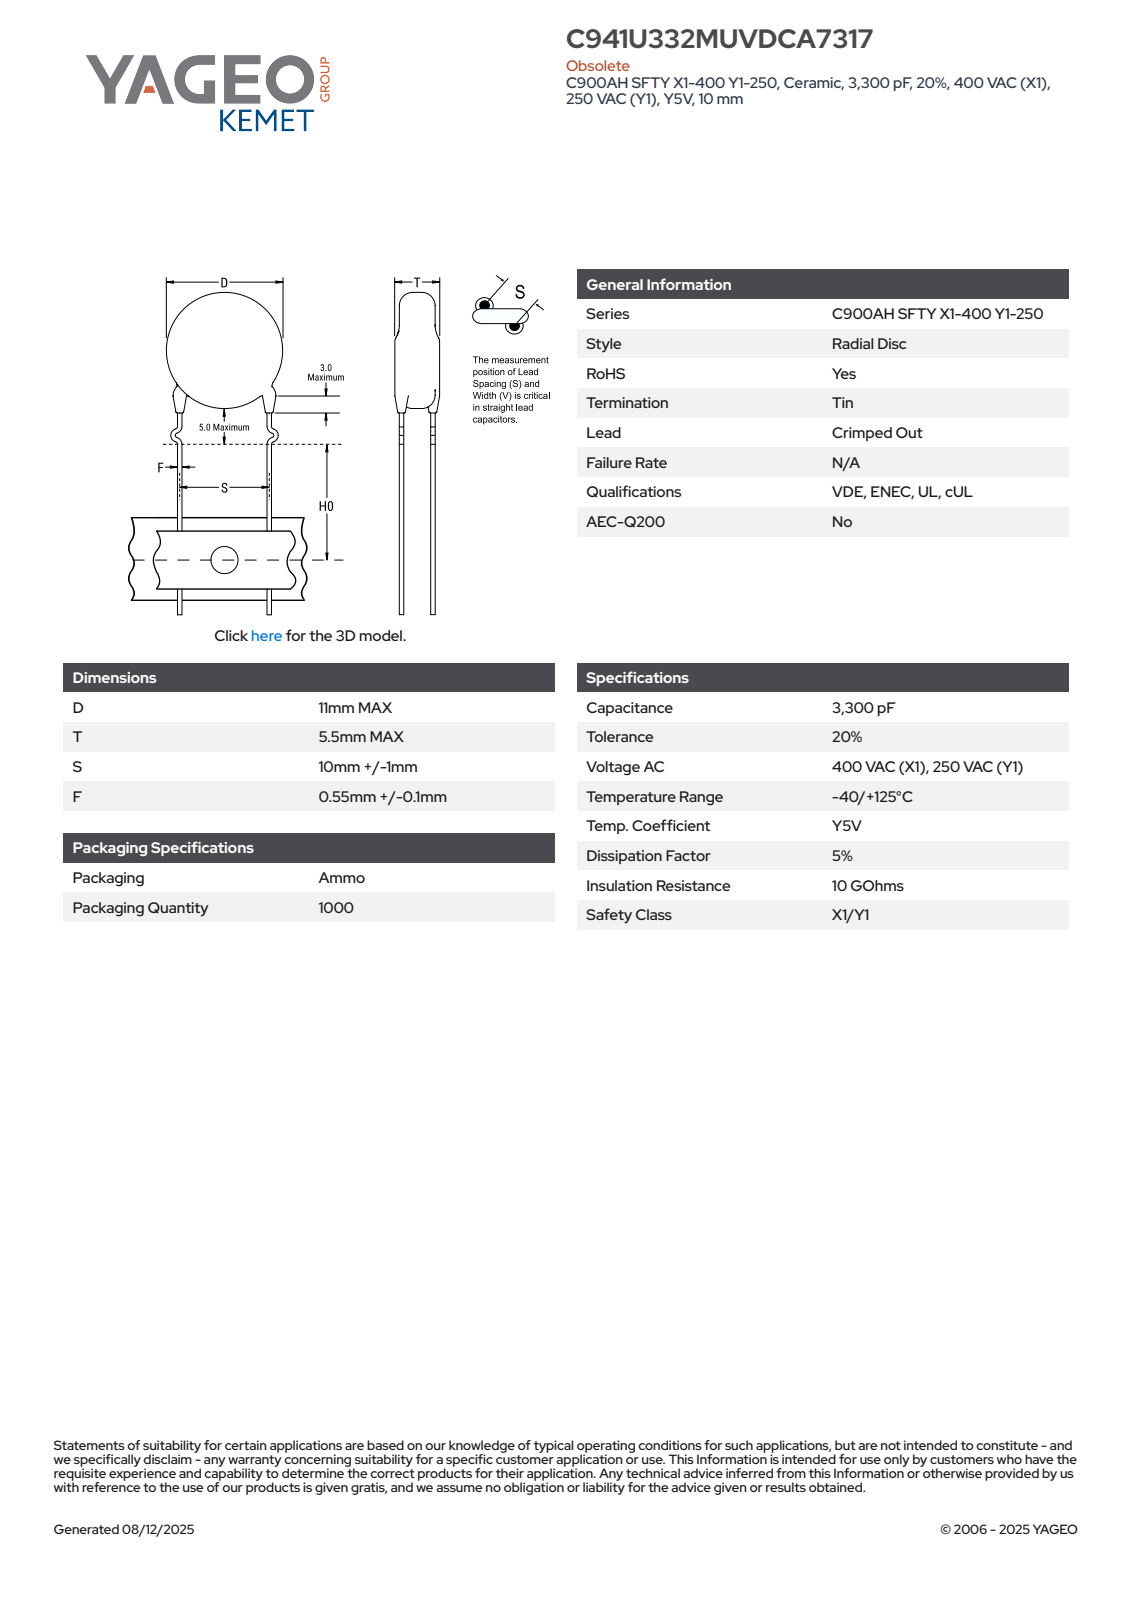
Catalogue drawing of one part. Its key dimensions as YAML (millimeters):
part_name: "CCD_KCOC900_D11T5.5S10LL20F0.55"
step_written_by: "SolidWorks 2014 (AUTOMOTIVE_DESIGN)"
units: millimeters
bodies: {solids: 4, faces: 87, planar: 63, cylindrical: 6, other: 18}
overall_size: [36, 14.69, 5.5]
volume: 533
surface_area: 489
round_bosses_or_shafts:
  - {diameter: 1.2, count: 2}
  - {diameter: 11, count: 1}
face_to_face_distances: [5.5, 1.14, 6.08, 4.94, 0.32, 0.92, 4.67, 2.36, 3.39, 3.53]
